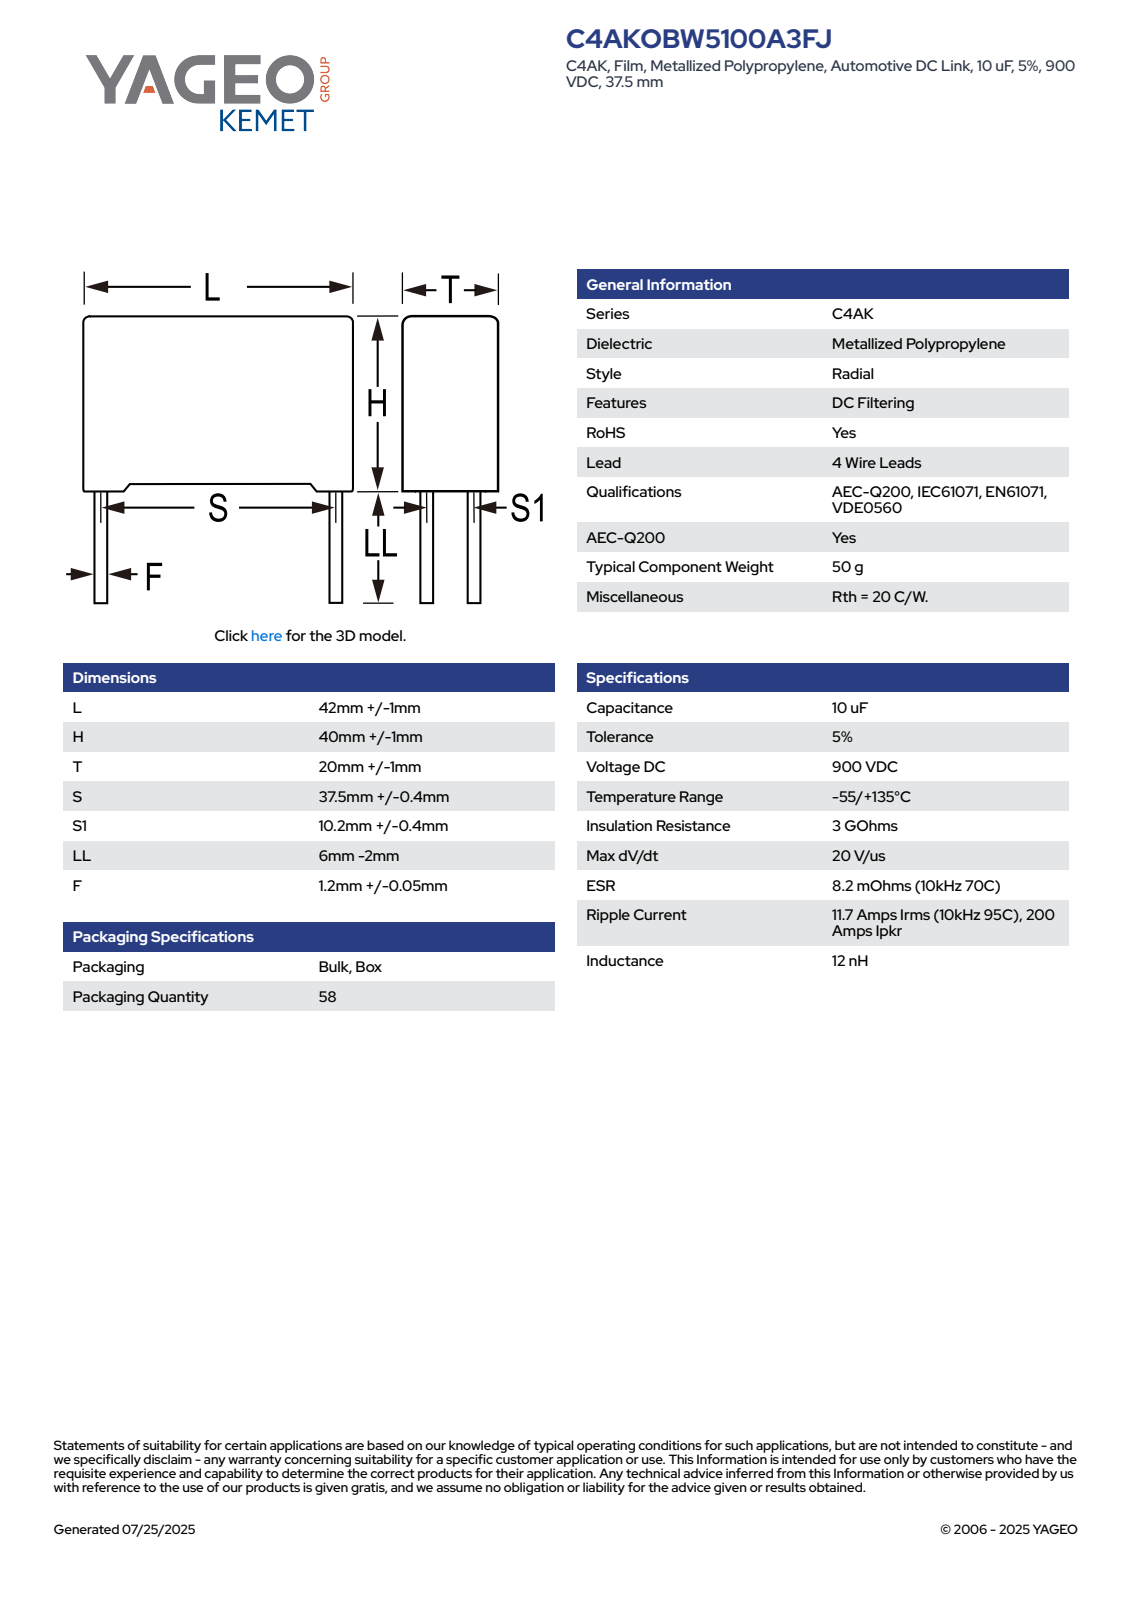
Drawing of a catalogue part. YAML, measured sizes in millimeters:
part_name: "CFP_RB4_42X40X20_L43H41T21S37.5S110.2LL4F1.25"
step_written_by: "SolidWorks 2014 (AUTOMOTIVE_DESIGN)"
units: millimeters
bodies: {solids: 4, faces: 87, planar: 79, cylindrical: 8, other: 0}
overall_size: [45, 43, 21]
volume: 36065
surface_area: 7266
round_bosses_or_shafts:
  - {diameter: 1.25, count: 4}
face_to_face_distances: [21, 43, 39.79, 1.21, 41, 1.29, 21.01, 41.71, 19.71, 40.42]
